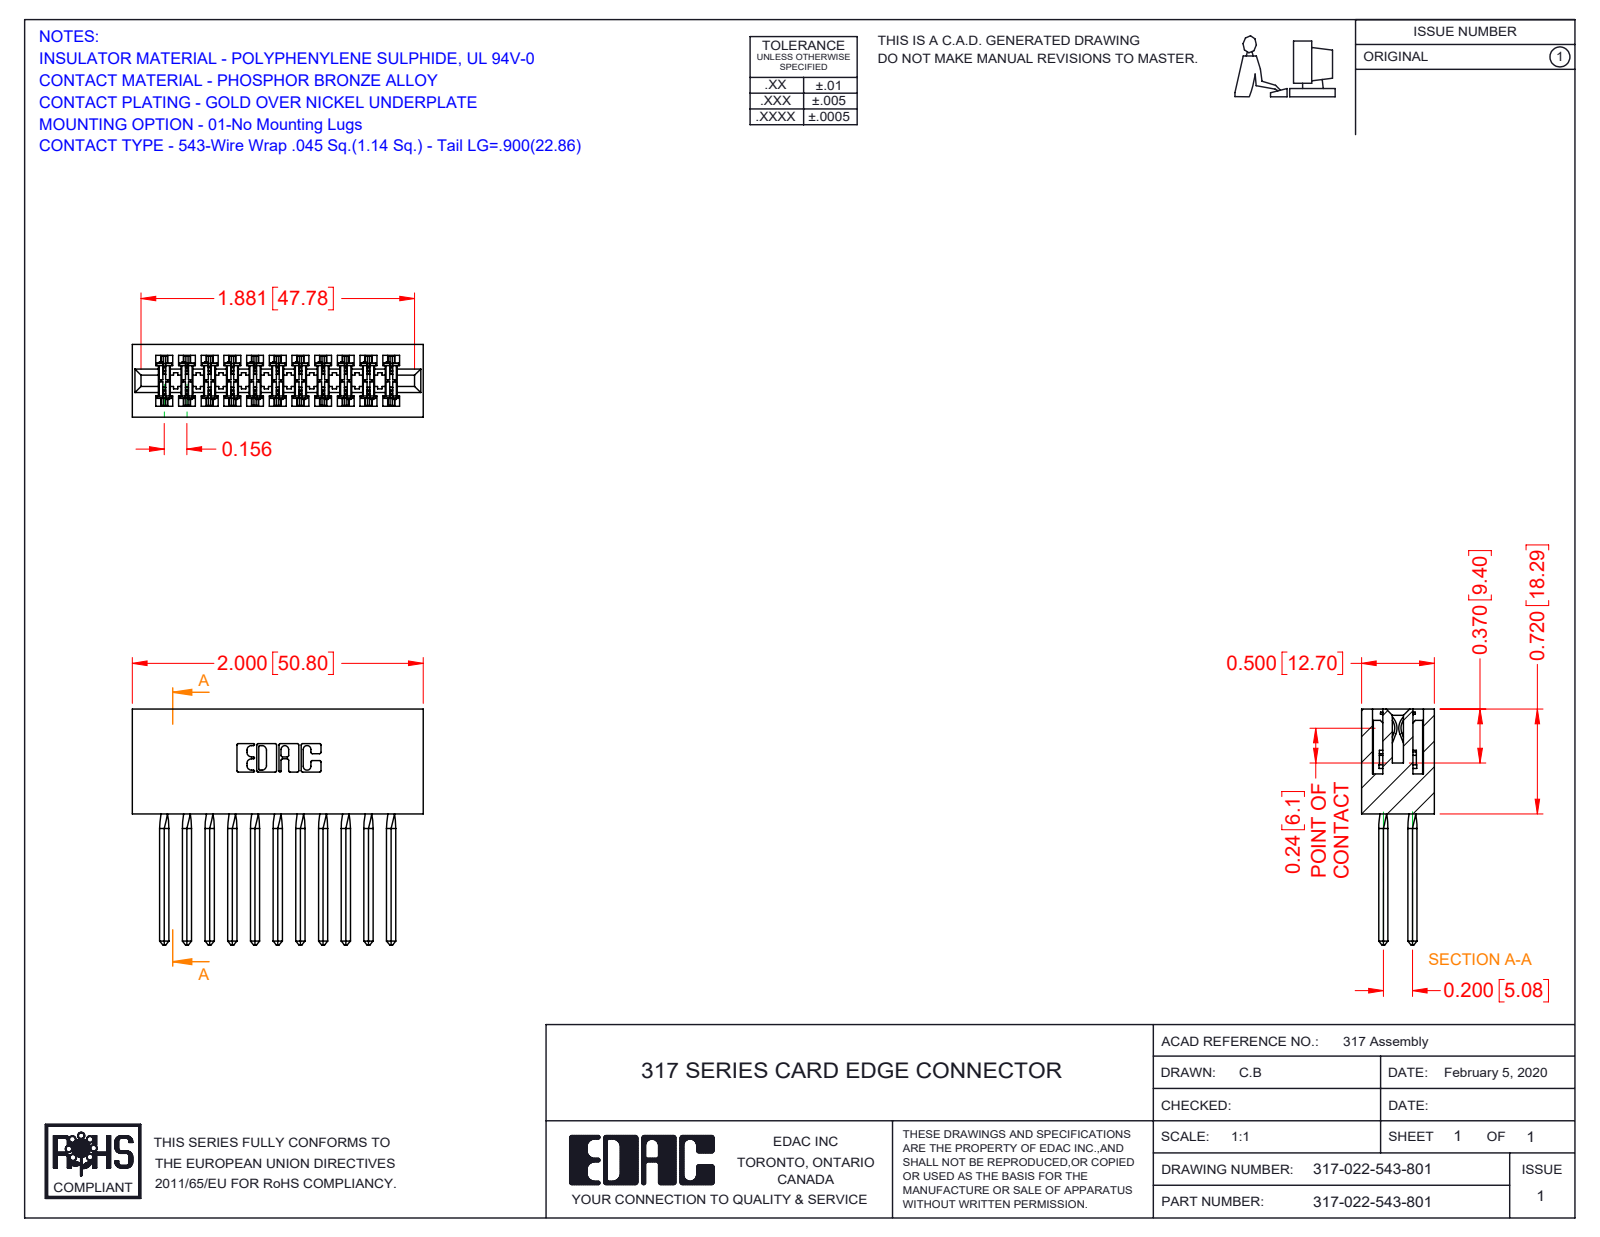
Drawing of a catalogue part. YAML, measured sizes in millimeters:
part_name: "317-290-001_543; 317 Part_Lugless; 317-022-543-801"
step_written_by: "SolidWorks 2016 (CONFIG_CONTROL_DESIGN)"
units: millimeters
bodies: {solids: 23, faces: 2048, planar: 1656, cylindrical: 304, other: 88}
overall_size: [50.8, 41.1, 12.7]
volume: 9370
surface_area: 13290
partial_cylinders:
  - {radius: 0.4, count: 44}
  - {radius: 0.3, count: 22}
  - {radius: 0.2, count: 6}
  - {radius: 0.8, count: 6}
  - {radius: 0.7, count: 3}
  - {radius: 2.4, count: 2}
  - {radius: 2.5, count: 2}
  - {radius: 2.8, count: 2}
face_to_face_distances: [12.7, 1.9, 2.8, 10.8, 5.6, 4, 8.4, 2.9, 8.9, 15.8]
